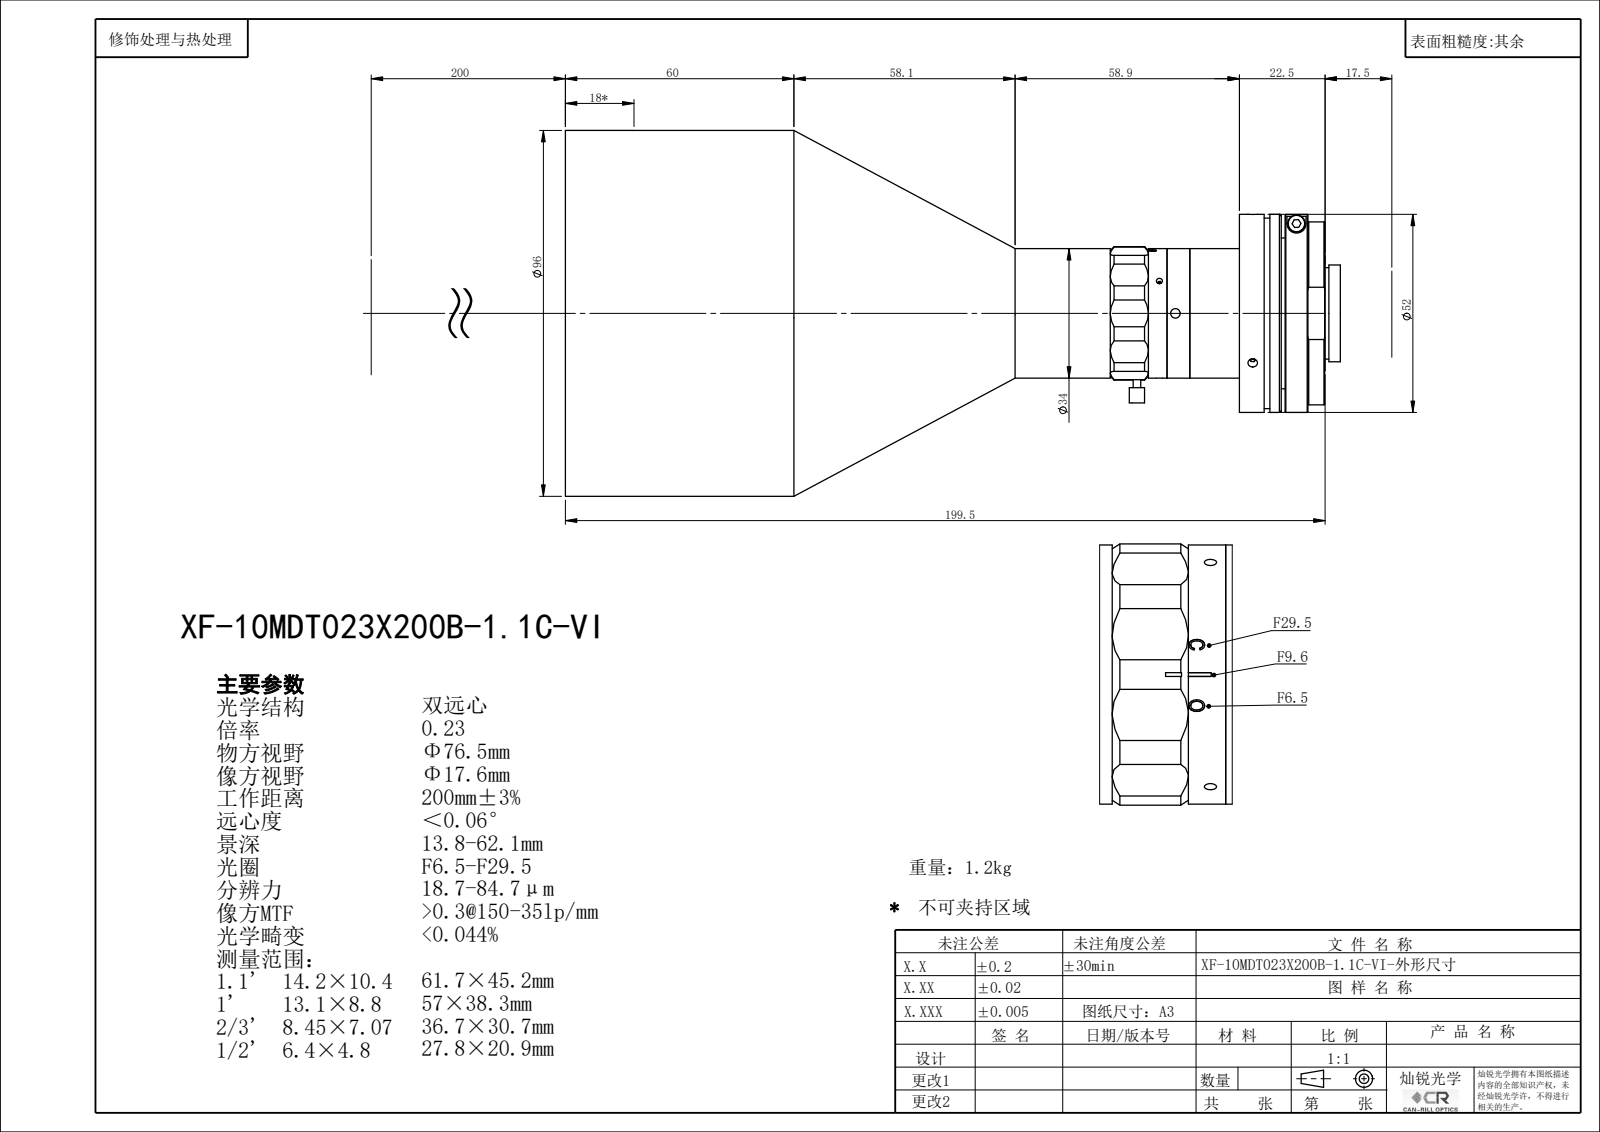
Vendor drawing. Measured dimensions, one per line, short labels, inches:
name: XF-10MDT023X200B-1.1C-VI
written by: SolidWorks 2022 (CONFIG_CONTROL_DESIGN)
unit: in
bodies: 0 solids, 208 faces (66 planar, 100 cylindrical, 42 other)
size: 8.011 × 3.78 × 3.78
holes: 3× ⌀0.063, 3× ⌀0.098, 1× ⌀0.081, 1× ⌀0.118, 1× ⌀0.882, 1× ⌀0.906, 1× ⌀1.079, 1× ⌀1.472, 1× ⌀3.465, 1× ⌀3.583
bosses: 2× ⌀0.079, 1× ⌀3.78, 1× ⌀2.047, 1× ⌀1.969, 1× ⌀1.89, 1× ⌀1.339, 1× ⌀1.181, 1× ⌀1
rounds: 10× R0.394, 3× R0.157, 1× R0.079, 1× R0.098, 1× R0.665, 1× R0.689, 1× R0.827
face distances: 0.882, 0.433, 0.449, 6.968, 7.401, 7.85, 0.354, 6.614, 7.047, 7.496
hole spacings: 0.965
